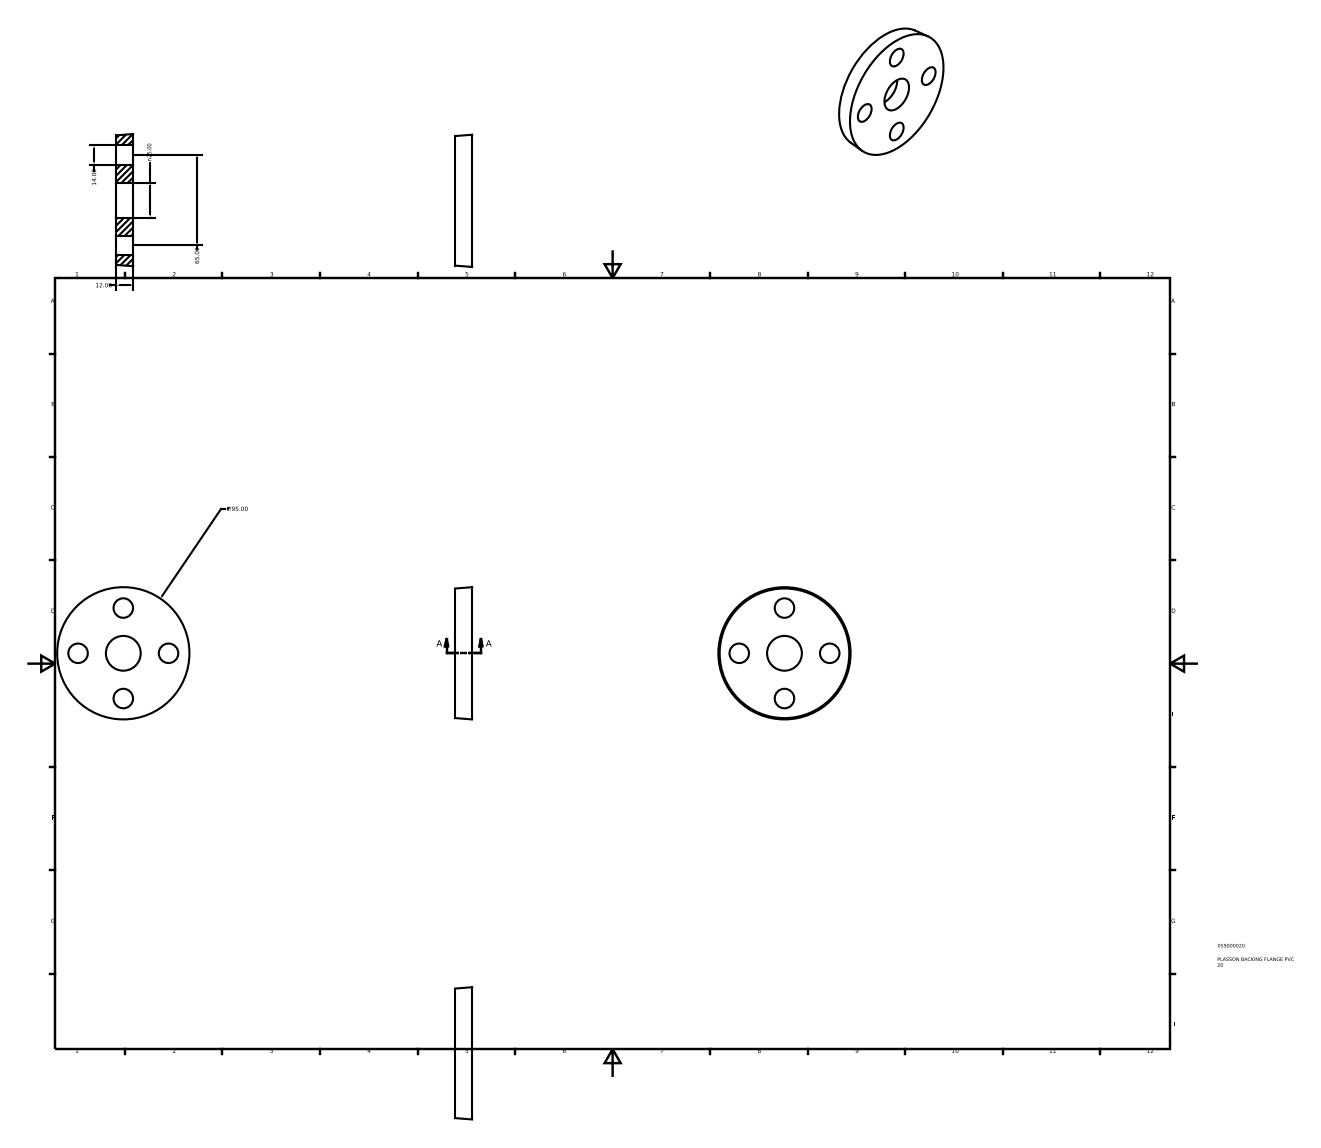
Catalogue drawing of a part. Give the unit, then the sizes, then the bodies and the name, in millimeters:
Units: millimetres
Overall size (bounding box): 95 × 95 × 12
Round holes (diameter × count): ⌀14 ×4, ⌀25 ×1
Main face-to-face distances: 12
Hole centre spacings: 32.5, 45.96, 65
Volume: 70 089 mm³ · Surface area: 18 293 mm²
Bodies: 1 solid, 8 faces (2 planar, 5 cylindrical, 1 other)
Part name (STEP PRODUCT): 059000020
STEP written by: Autodesk Inventor 2015 (AUTOMOTIVE_DESIGN)
